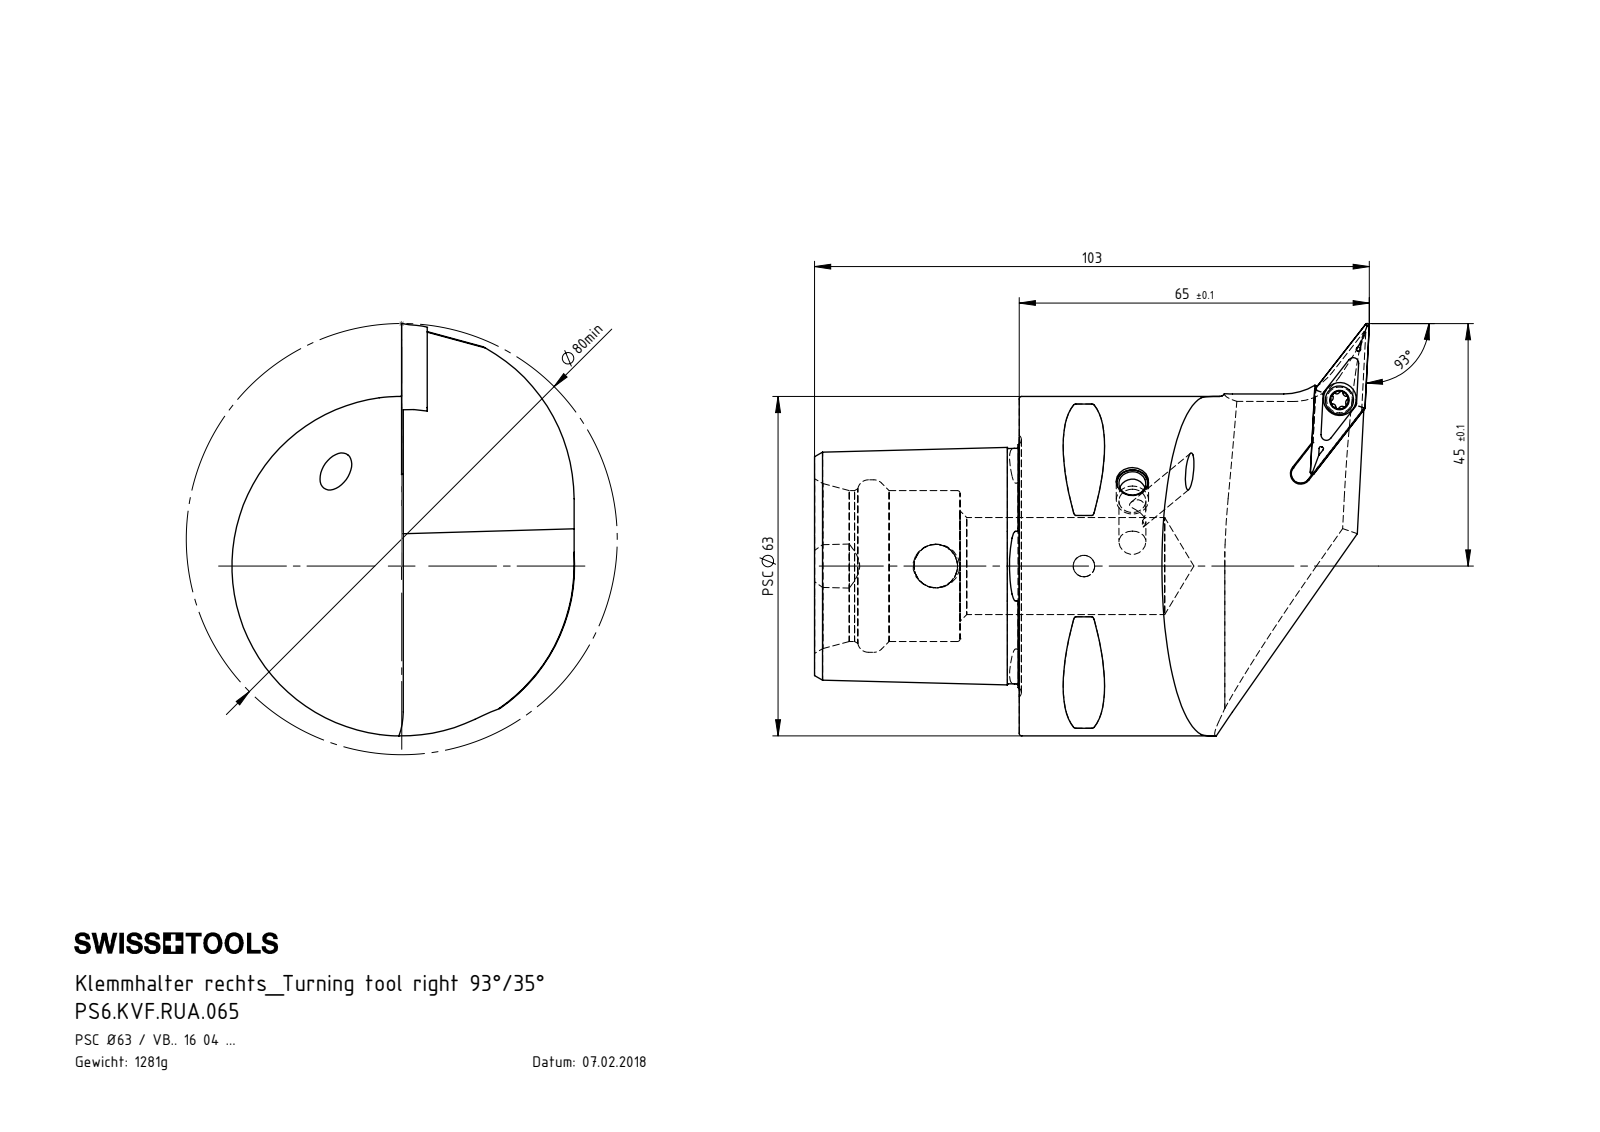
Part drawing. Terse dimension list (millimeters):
name: PS6-KVF.RUA.065_A; KVT_MB_600_060; VBMT160404; PS6.KVF.RUA.065 (+1 more)
written by: SolidWorks 2017 (AUTOMOTIVE_DESIGN)
unit: mm
bodies: 5 solids, 275 faces (56 planar, 70 cylindrical, 149 other)
size: 103 × 76.5 × 63.61
volume: 162 761 mm³; area: 28 489 mm²
holes: 2× ⌀5, 1× ⌀3.3, 1× ⌀4, 1× ⌀4.4, 1× ⌀6.1, 1× ⌀8.1, 1× ⌀18, 1× ⌀28, 1× ⌀32
bosses: 1× ⌀63, 1× ⌀6, 1× ⌀5.25, 1× ⌀4
rounds: 8× R0.5, 6× R0.34, 6× R0.59, 2× R0.15, 2× R6, 2× R32, 1× R1.75, 1× R11
face distances: 38, 24.88, 31.7, 27.24, 4.46, 27, 11, 55.8, 37.8, 10.8
hole spacings: 27.5, 56.57, 56.74, 81.03, 81.18
